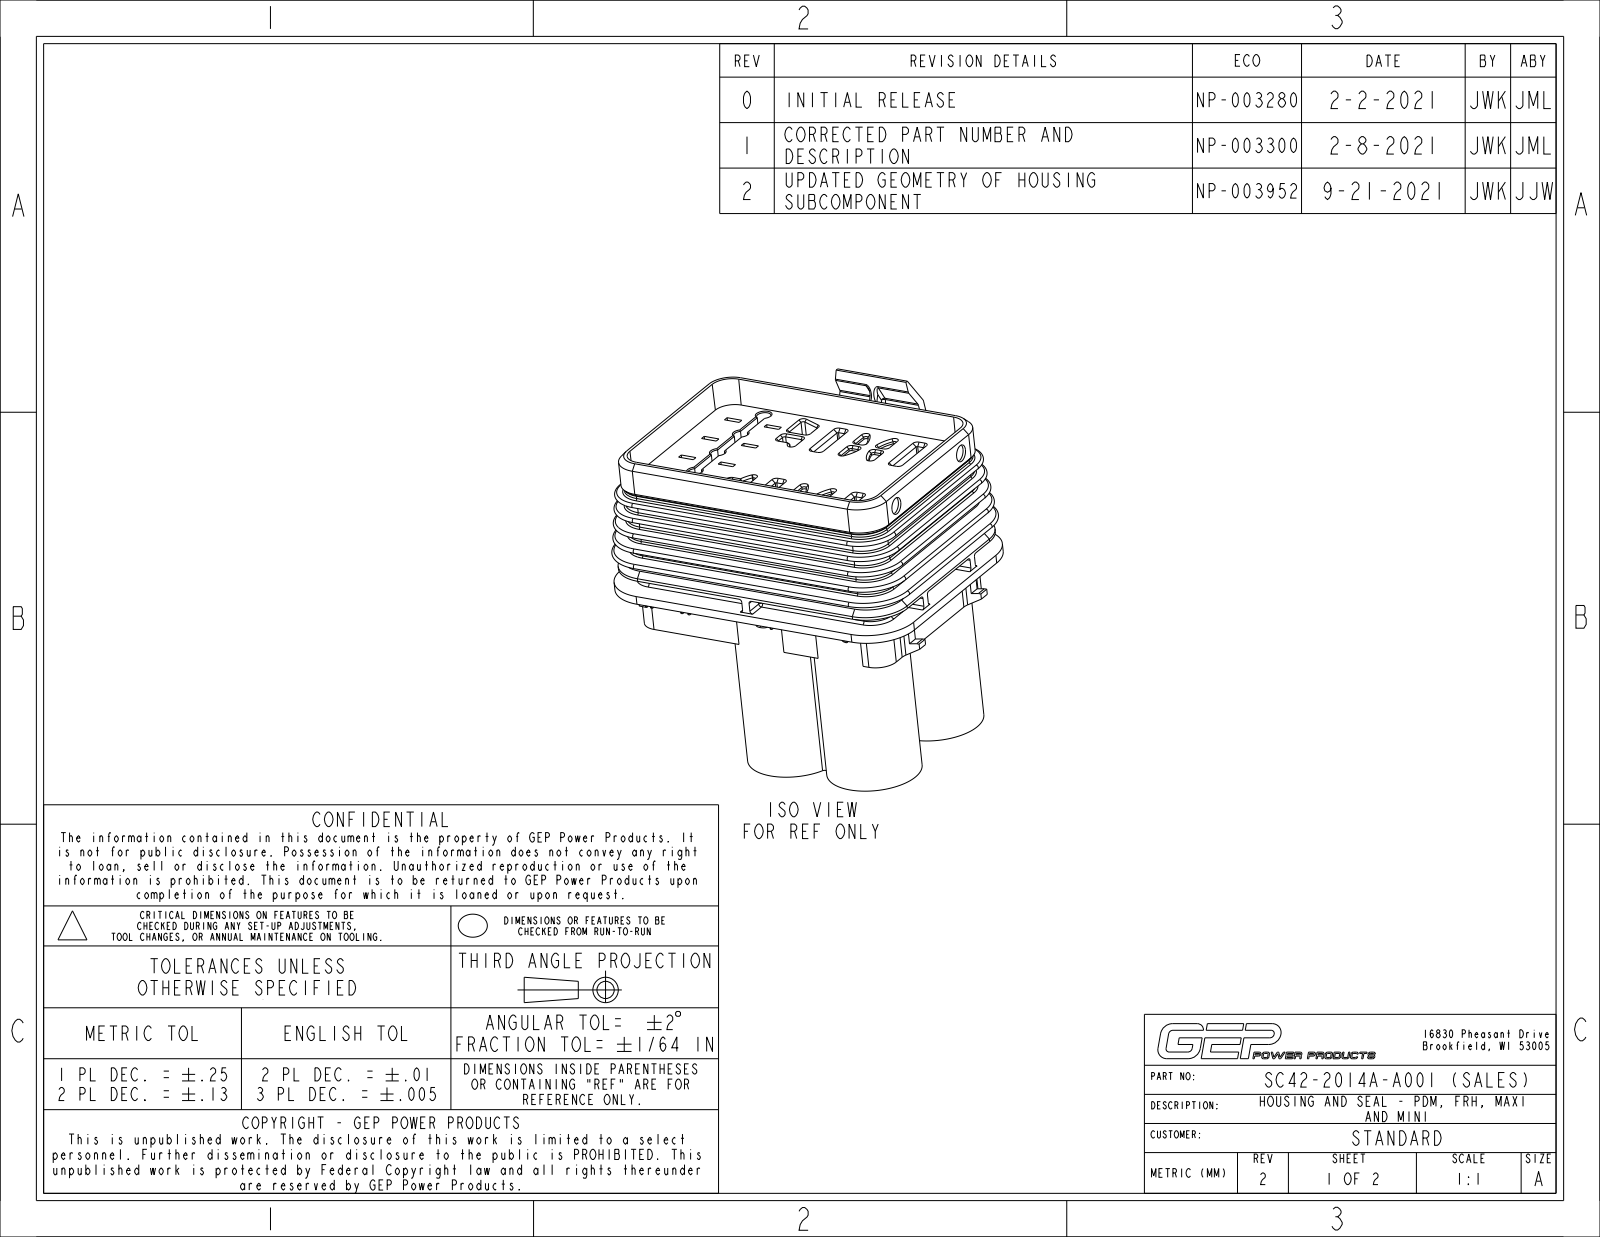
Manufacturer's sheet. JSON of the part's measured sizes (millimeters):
{"part_name": "PC26-2008A-B001_SALES_NCF; C14-1018_NCF_INSTALLED; PC42-2014A-A001_SALES_NCF_ASM; SC42-2014A-A001_NCF_ASM", "step_written_by": "CREO PARAMETRIC BY PTC INC, 2017110 (CONFIG_CONTROL_DESIGN)", "units": "millimeters", "bodies": {"solids": 2, "faces": 1592, "planar": 511, "cylindrical": 473, "other": 608}, "overall_size": [60, 57, 51.47], "volume_mm3": 55476, "surface_area_mm2": 42241, "round_holes": [[6.7, 8], [13.75, 4], [3, 2], [2.53, 1]], "round_bosses_or_shafts": [[16.75, 4]], "partial_cylinders_radius": [[0.5, 154], [0.4, 74], [0.3, 40], [0.2, 16], [3.5, 8], [4.4, 8], [4.5, 5], [5, 4]], "face_to_face_distances": [1.5, 0.8, 1, 16.2, 35.05, 1.55, 51, 35, 7.8, 24.7], "hole_center_spacings": [7.8, 11.24, 8.1, 15.6, 17.58, 4.76, 11.07, 16.2]}
